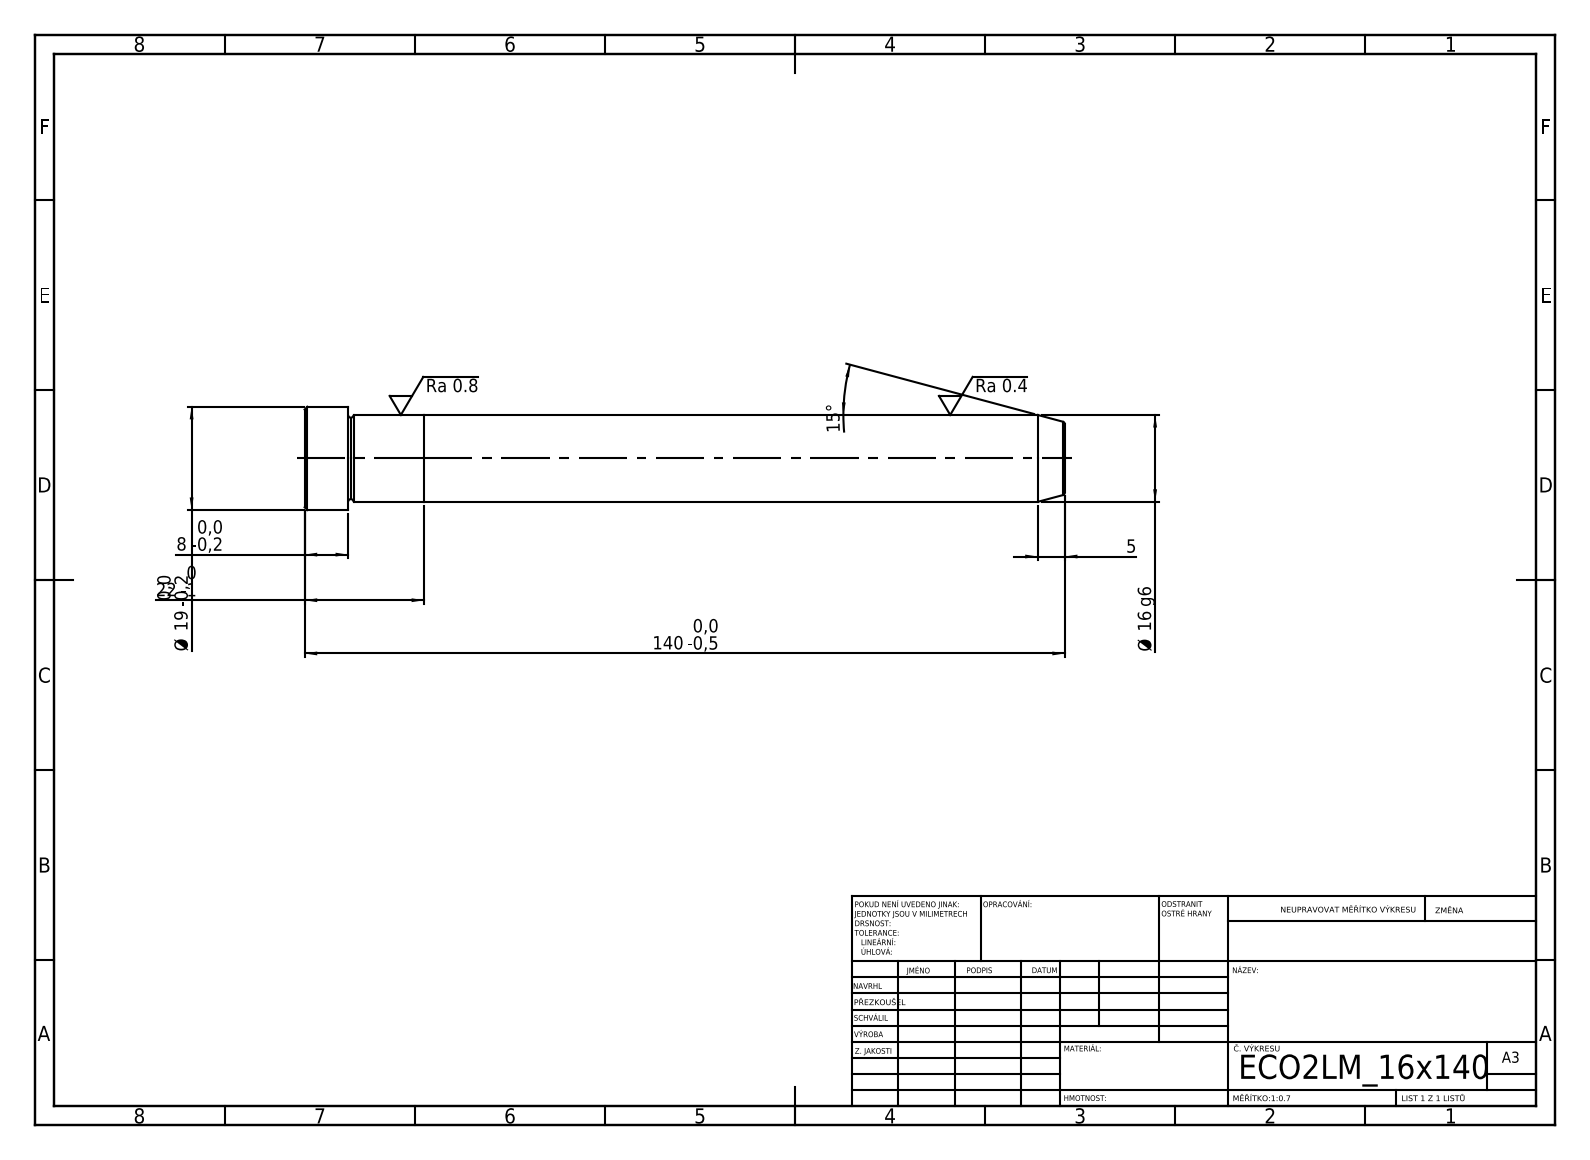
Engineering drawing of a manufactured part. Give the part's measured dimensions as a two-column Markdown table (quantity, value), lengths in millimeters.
| quantity | value |
| --- | --- |
| STEP written by | SolidWorks 2019 (CONFIG_CONTROL_DESIGN) |
| units | millimeters |
| bodies | 2 solids, 21 faces (5 planar, 6 cylindrical, 10 other) |
| overall size | 140 × 19 × 19 |
| volume | 28 622 mm³ |
| surface area | 8 010 mm² |
| round bosses / shafts (diameter × count) | 19 × 1, 16 × 1 |
| main face-to-face distances | 22, 118, 140, 132, 14, 8 |
